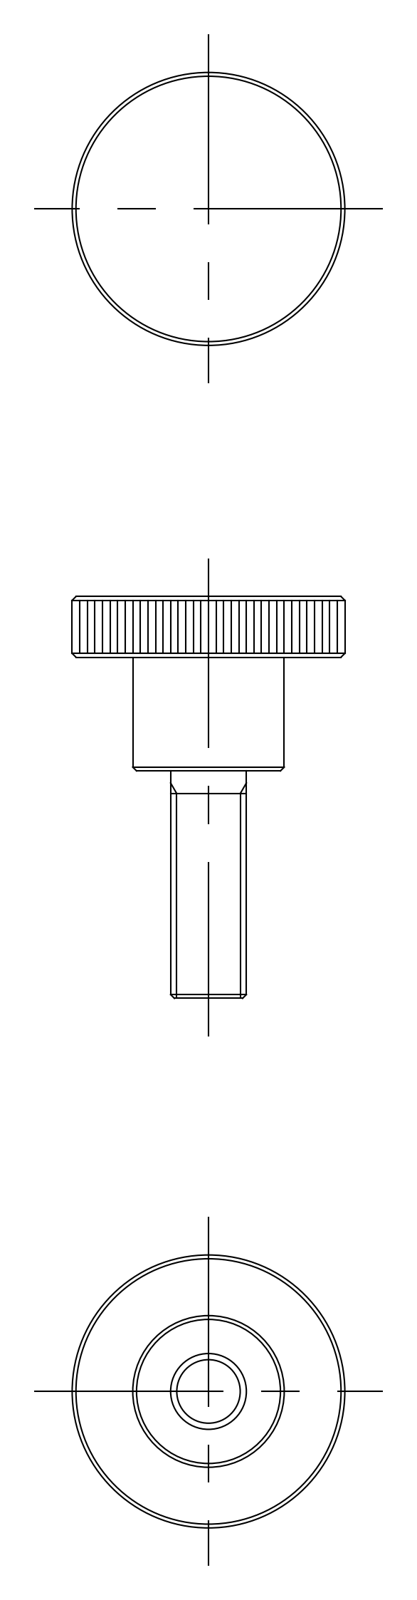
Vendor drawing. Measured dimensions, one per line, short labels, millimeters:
name: knob
written by: CADfix (AUTOMOTIVE_DESIGN)
unit: mm
bodies: 1 solid, 18 faces (0 planar, 0 cylindrical, 18 other)
size: 53 × 36 × 36
volume: 15 200 mm³; area: 4 732 mm²
